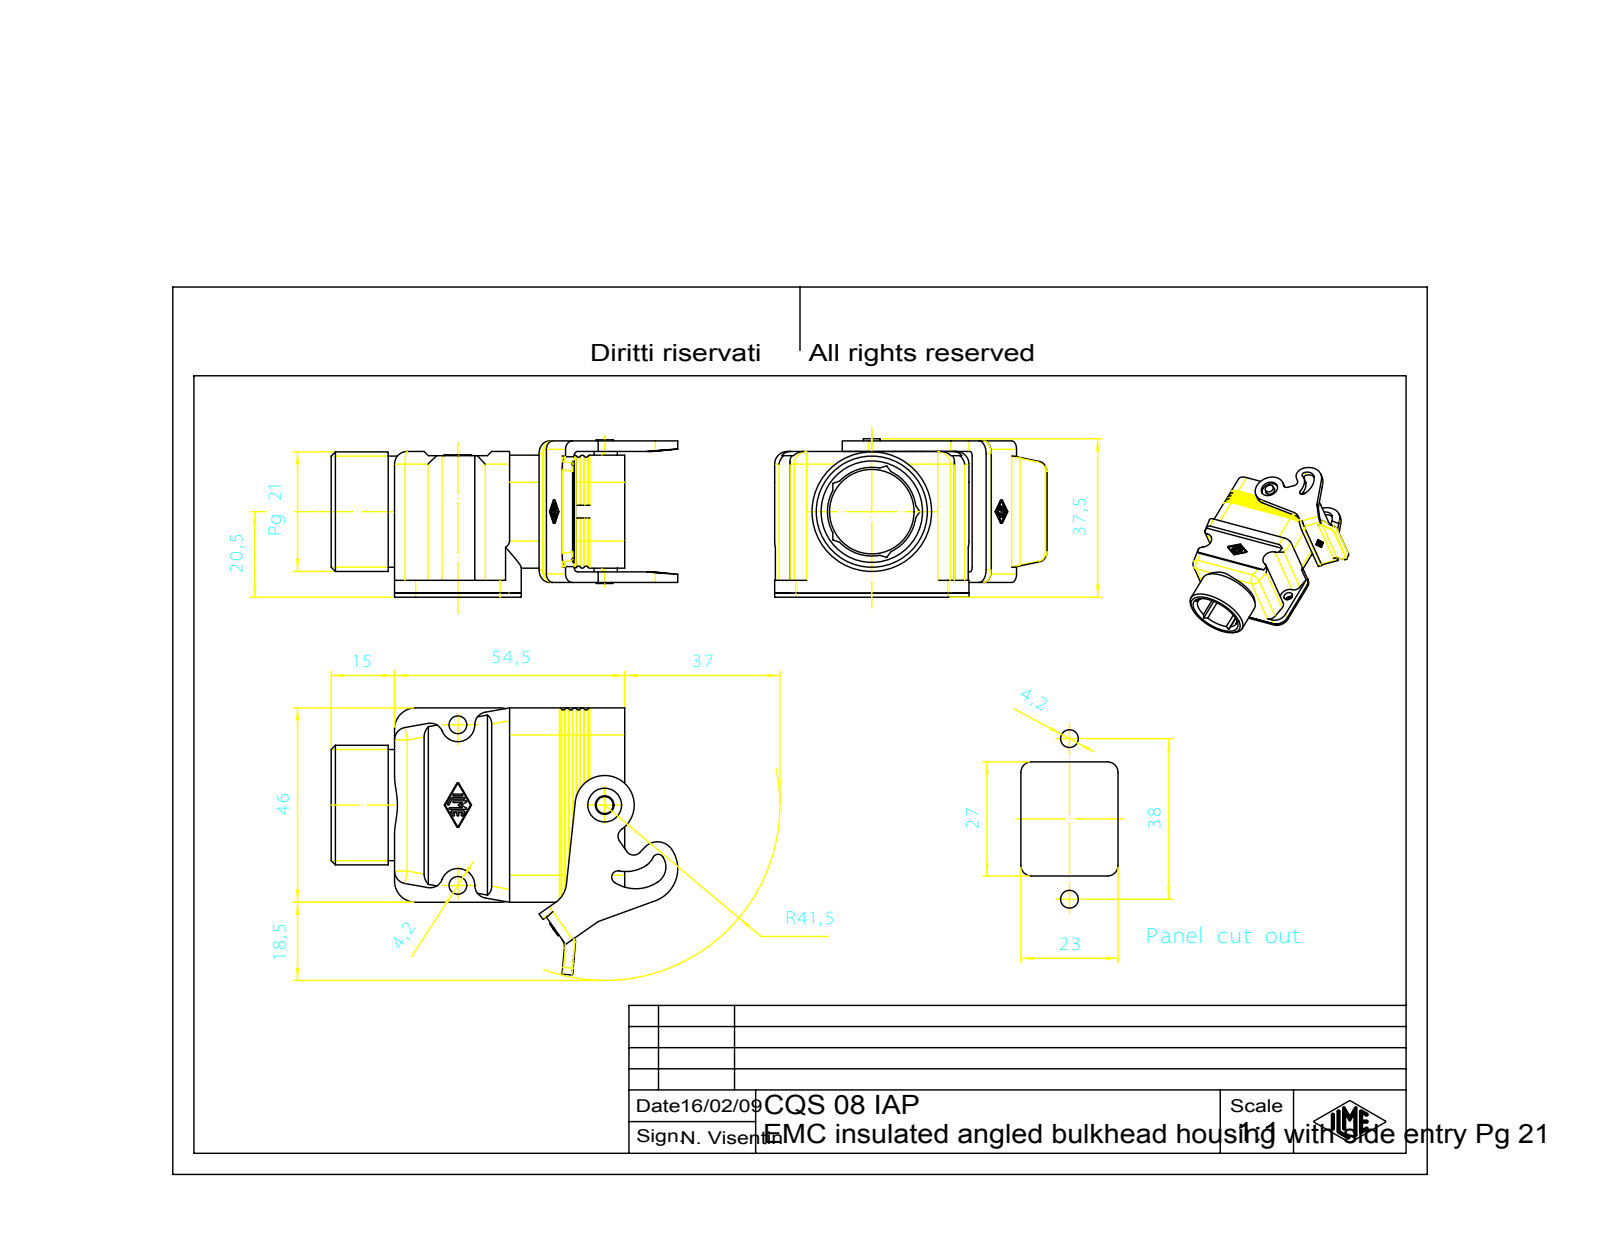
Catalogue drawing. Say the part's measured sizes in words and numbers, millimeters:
The part is named "CUSTODIA_CQ_08_IAP; LEVA_CQ_08_IAP; CQS_08_IAP". Its 3-D file was written by "CoCreate Modeling 16.00A 16-Aug-2008 (C) Parametric Technology GmbH (AUTOMOTIVE_DESIGN)". It is 2 solids with 721 faces: 282 planar, 293 cylindrical and 146 other. Overall it measures 82.05 by 63.2 by 37.25 millimeters. Its volume is 30 860 cubic millimeters and its surface area 25 762 square millimeters. Round holes: 4 of diameter 2.4, 4 of diameter 2.5, 4 of diameter 3.1, 2 of diameter 4.2, 1 of diameter 4.4, 1 of diameter 8, 1 of diameter 20. Round bosses or shafts: 1 of diameter 28.3, 1 of diameter 26.31, 1 of diameter 4. Partial cylindrical surfaces (rounded edges, fillets, slot ends): 36 of radius 0.5, 14 of radius 0.1, 14 of radius 3, 13 of radius 0.2, 9 of radius 2, 5 of radius 2.5, 4 of radius 1.7, 4 of radius 4.5. The main face-to-face distances are 2.5, 27.5, 33.5, 2.75, 25.75, 2, 3.5, 5.25, 28.25, 31. The hole center spacings are 7.3, 13.4, 17.44, 32.2, 34.88, 35.73, 32.34, 39.61.
